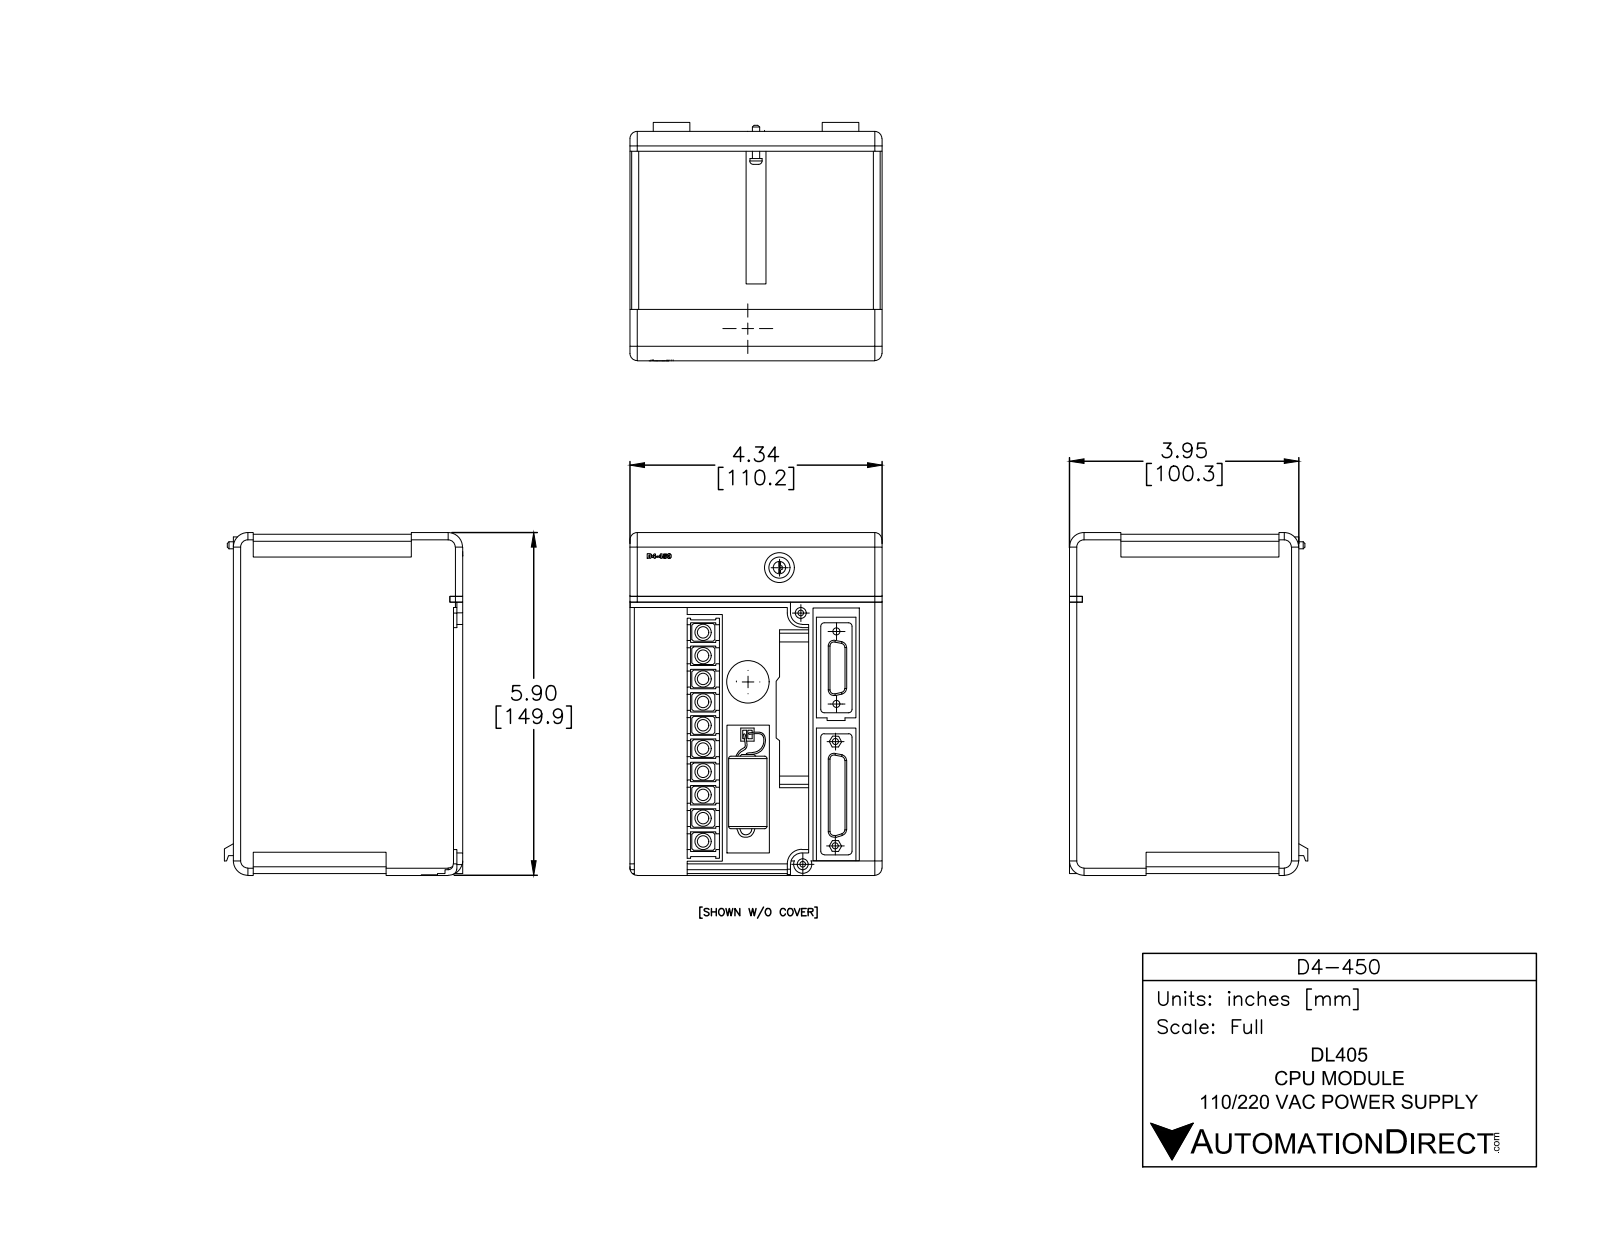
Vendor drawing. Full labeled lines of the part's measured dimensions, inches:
Part name (STEP PRODUCT): D4-450
STEP written by: SolidWorks 2014 (AUTOMOTIVE_DESIGN)
Units: inches
Bodies: 2 solids, 816 faces (608 planar, 128 cylindrical, 80 other)
Overall size (bounding box): 5.905 × 4.34 × 4.106
Volume: 89.68 in³ · Surface area: 181.8 in²
Round holes (diameter × count): ⌀0.1 ×2, ⌀0.12 ×2, ⌀0.104 ×1, ⌀0.105 ×1, ⌀0.188 ×1, ⌀0.188 ×1, ⌀0.216 ×1, ⌀0.51 ×1
Round bosses / shafts (diameter × count): ⌀0.279 ×10, ⌀0.055 ×4, ⌀0.055 ×2, ⌀0.567 ×1, ⌀0.365 ×1, ⌀0.212 ×1, ⌀0.137 ×1, ⌀0.123 ×1
Partial cylindrical surfaces — rounded edges, fillets, slot ends (radius × count): R0.1 ×9, R0.06 ×8, R0.125 ×8, R0.03 ×6, R0.25 ×6, R0.12 ×4, R0.028 ×2, R0.2 ×2
Main face-to-face distances: 4.34, 0.03, 5.845, 5.875, 3.95, 0.715, 3.235, 0.45, 0.115, 5.905
Hole centre spacings: 0.644, 0.649, 0.69, 0.861, 1.248, 1.47, 1.681, 1.798
